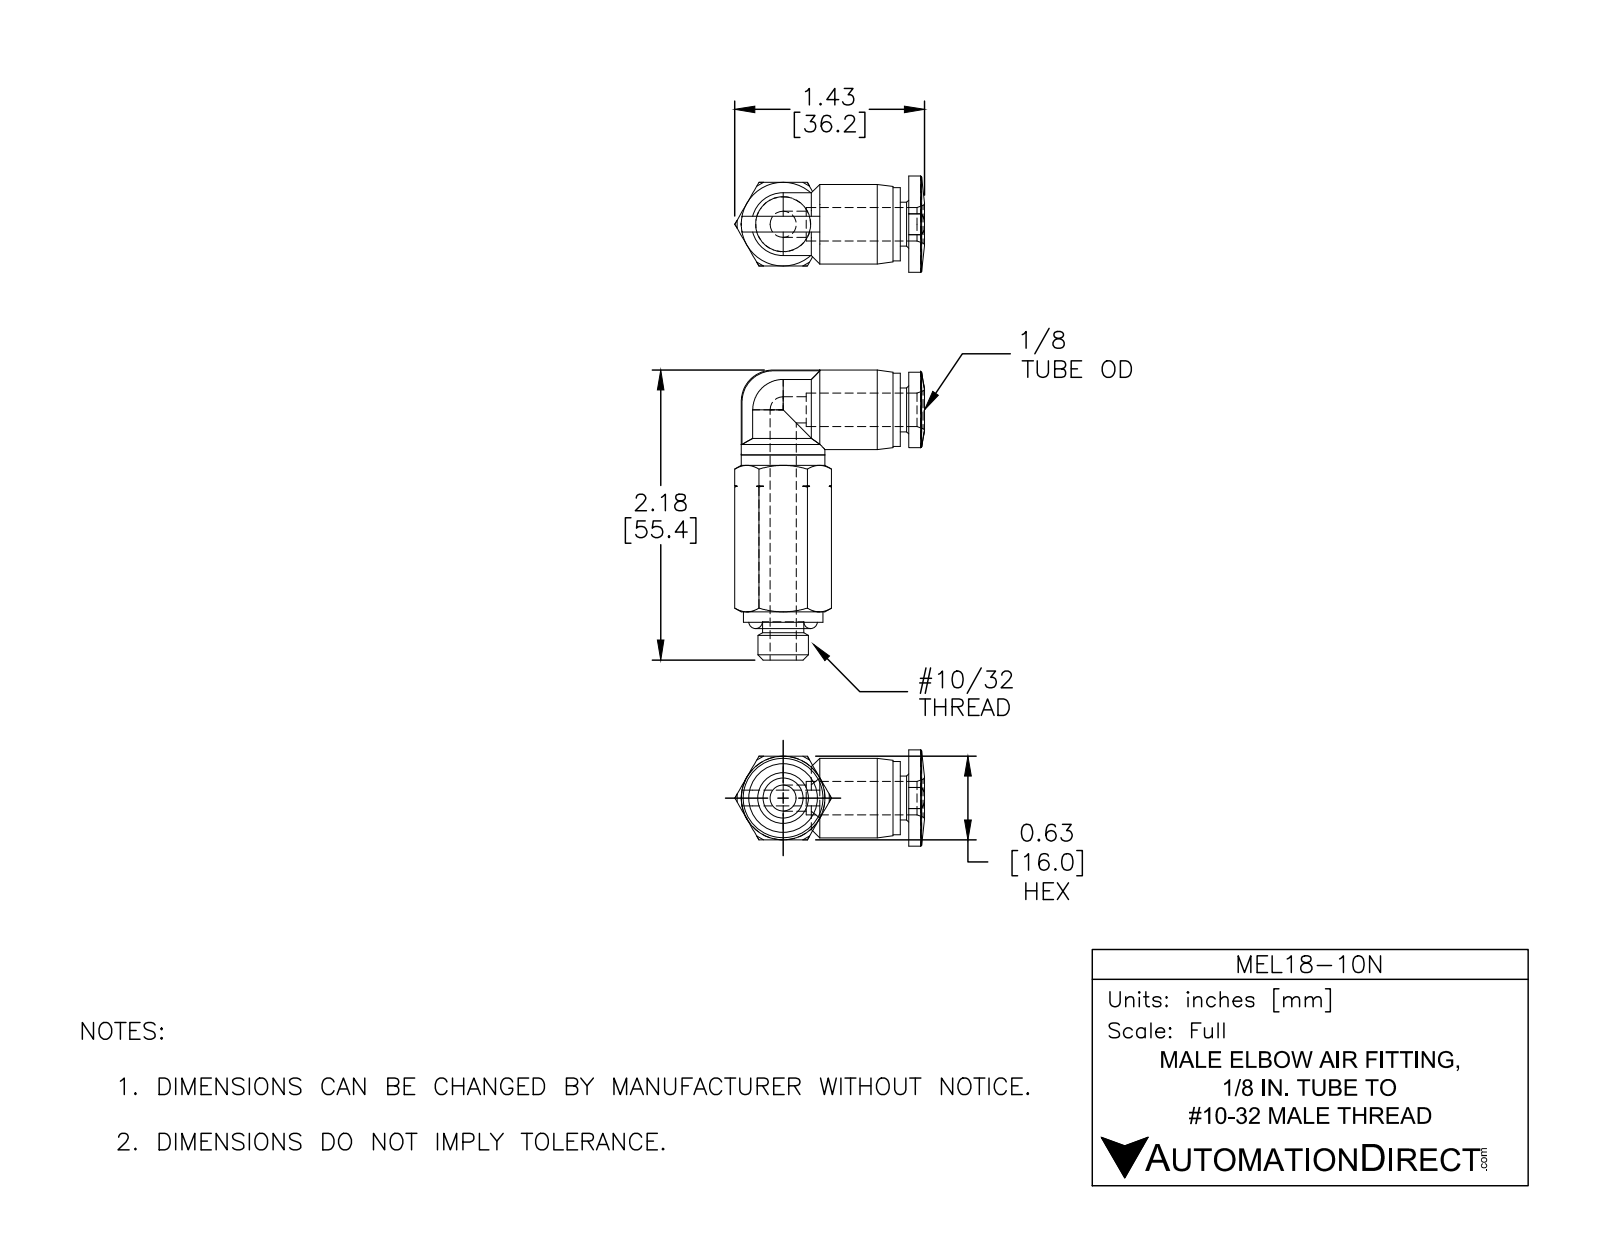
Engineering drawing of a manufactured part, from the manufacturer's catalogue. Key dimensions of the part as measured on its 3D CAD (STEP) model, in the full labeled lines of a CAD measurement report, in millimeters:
Part name (STEP PRODUCT): MEL18-10N
STEP written by: SolidWorks 2015 (CONFIG_CONTROL_DESIGN)
Units: millimetres
Bodies: 2 solids, 123 faces (22 planar, 32 cylindrical, 69 other)
Overall size (bounding box): 27.7 × 18.1 × 9.2
Volume: 1 400 mm³ · Surface area: 1 470 mm²
Round holes (diameter × count): ⌀2.5 ×2, ⌀3.2 ×1
Round bosses / shafts (diameter × count): ⌀7.6 ×2, ⌀8 ×1, ⌀8 ×1, ⌀7 ×1, ⌀4.8 ×1, ⌀4.2 ×1, ⌀4 ×1
Partial cylindrical surfaces — rounded edges, fillets, slot ends (radius × count): R3 ×2, R3.6 ×2
Main face-to-face distances: 8, 0.8, 3.3, 4.7, 1.5, 0.7, 3.6, 4.3, 4.6, 1
